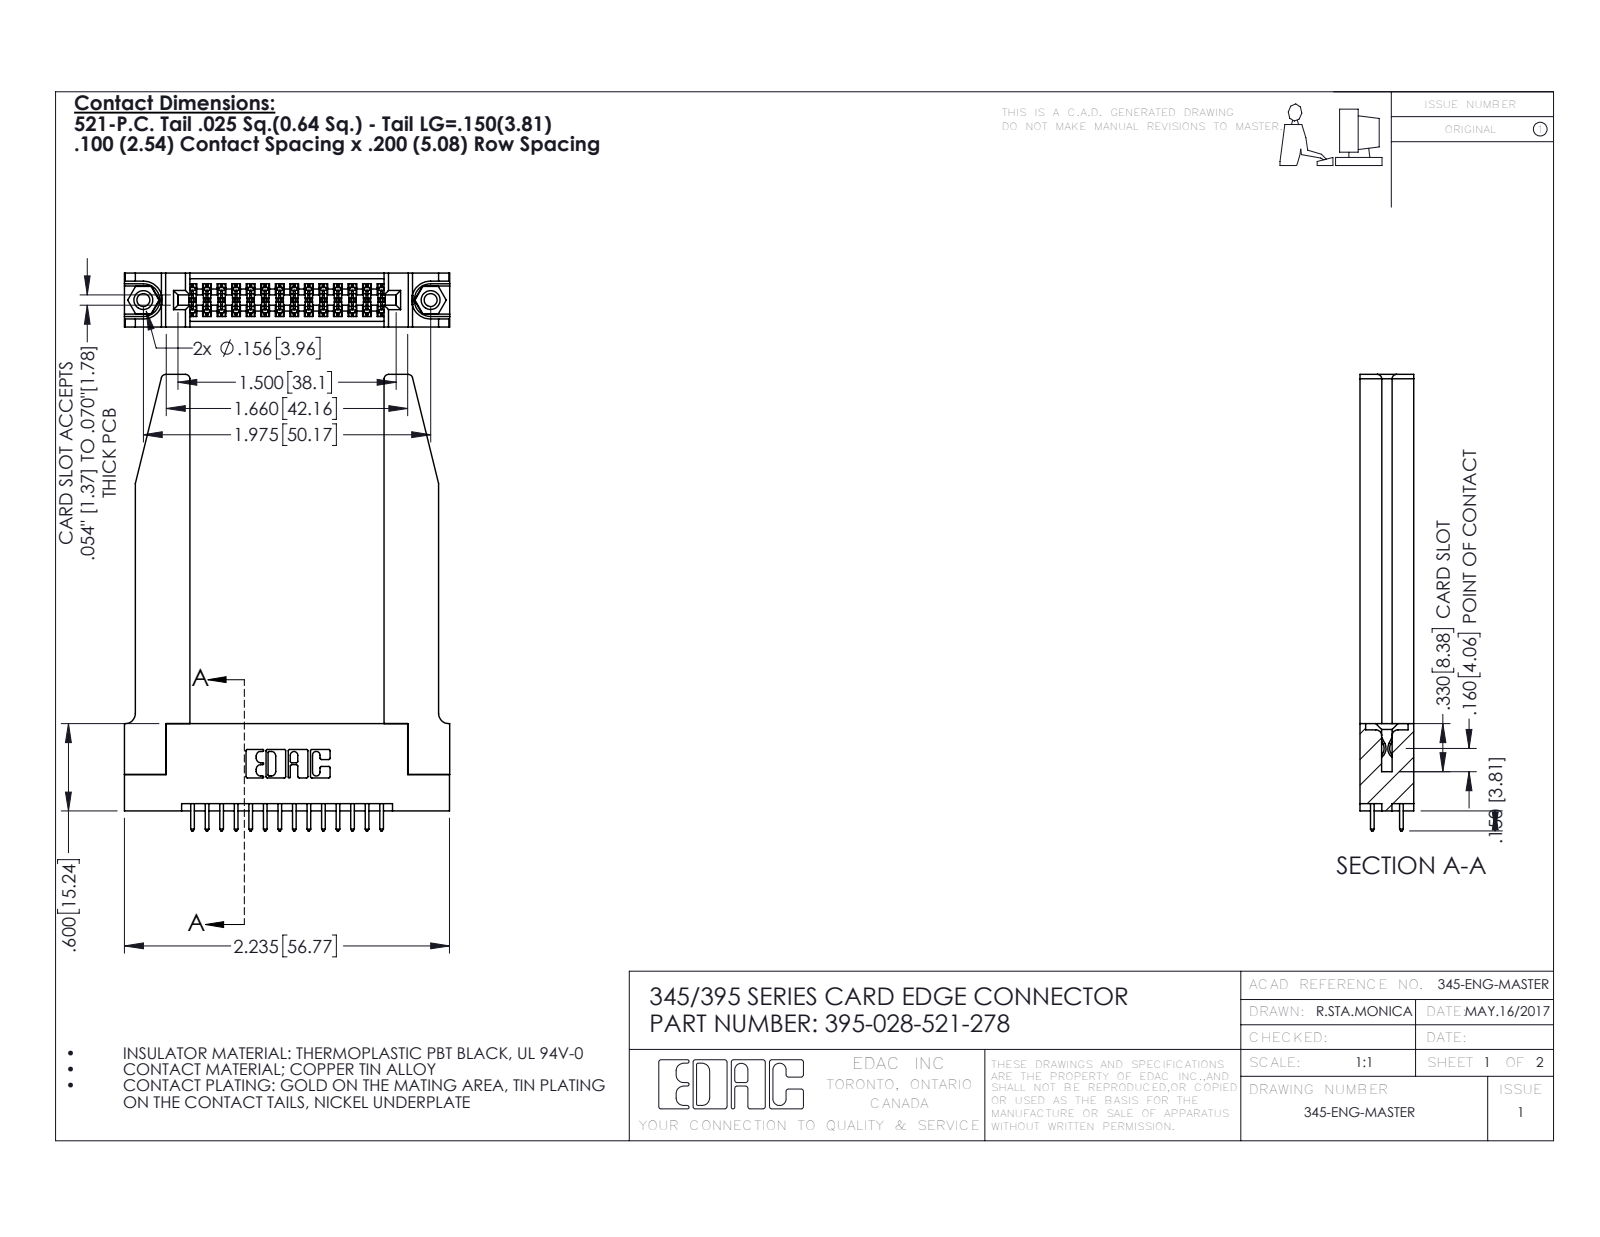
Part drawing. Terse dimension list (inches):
name: 345 Part_Flush Mounting Lugs - 0.156 Dia-TH; 345-220-078_345-220-078; 395-028-521-278; 345-292-001_345-293-121 (+1 more)
written by: SolidWorks 2016 (CONFIG_CONTROL_DESIGN)
unit: in
bodies: 33 solids, 1760 faces (1146 planar, 562 cylindrical, 52 other)
size: 3.137 × 2.236 × 0.37
volume: 0.794 in³; area: 21.66 in²
holes: 2× ⌀0.089, 2× ⌀0.125, 2× ⌀0.156, 1× ⌀0.064
bosses: 2× ⌀0.155
rounds: 42× R0.006, 28× R0.01, 22× R0.01, 8× R0.03, 6× R0.007, 6× R0.031, 3× R0.026, 2× R0.014
face distances: 0.37, 0.072, 0.298, 0.2, 0.148, 0.15, 0.098, 0.272, 0.025, 0.077
hole spacings: 0.27, 1.742, 1.975
